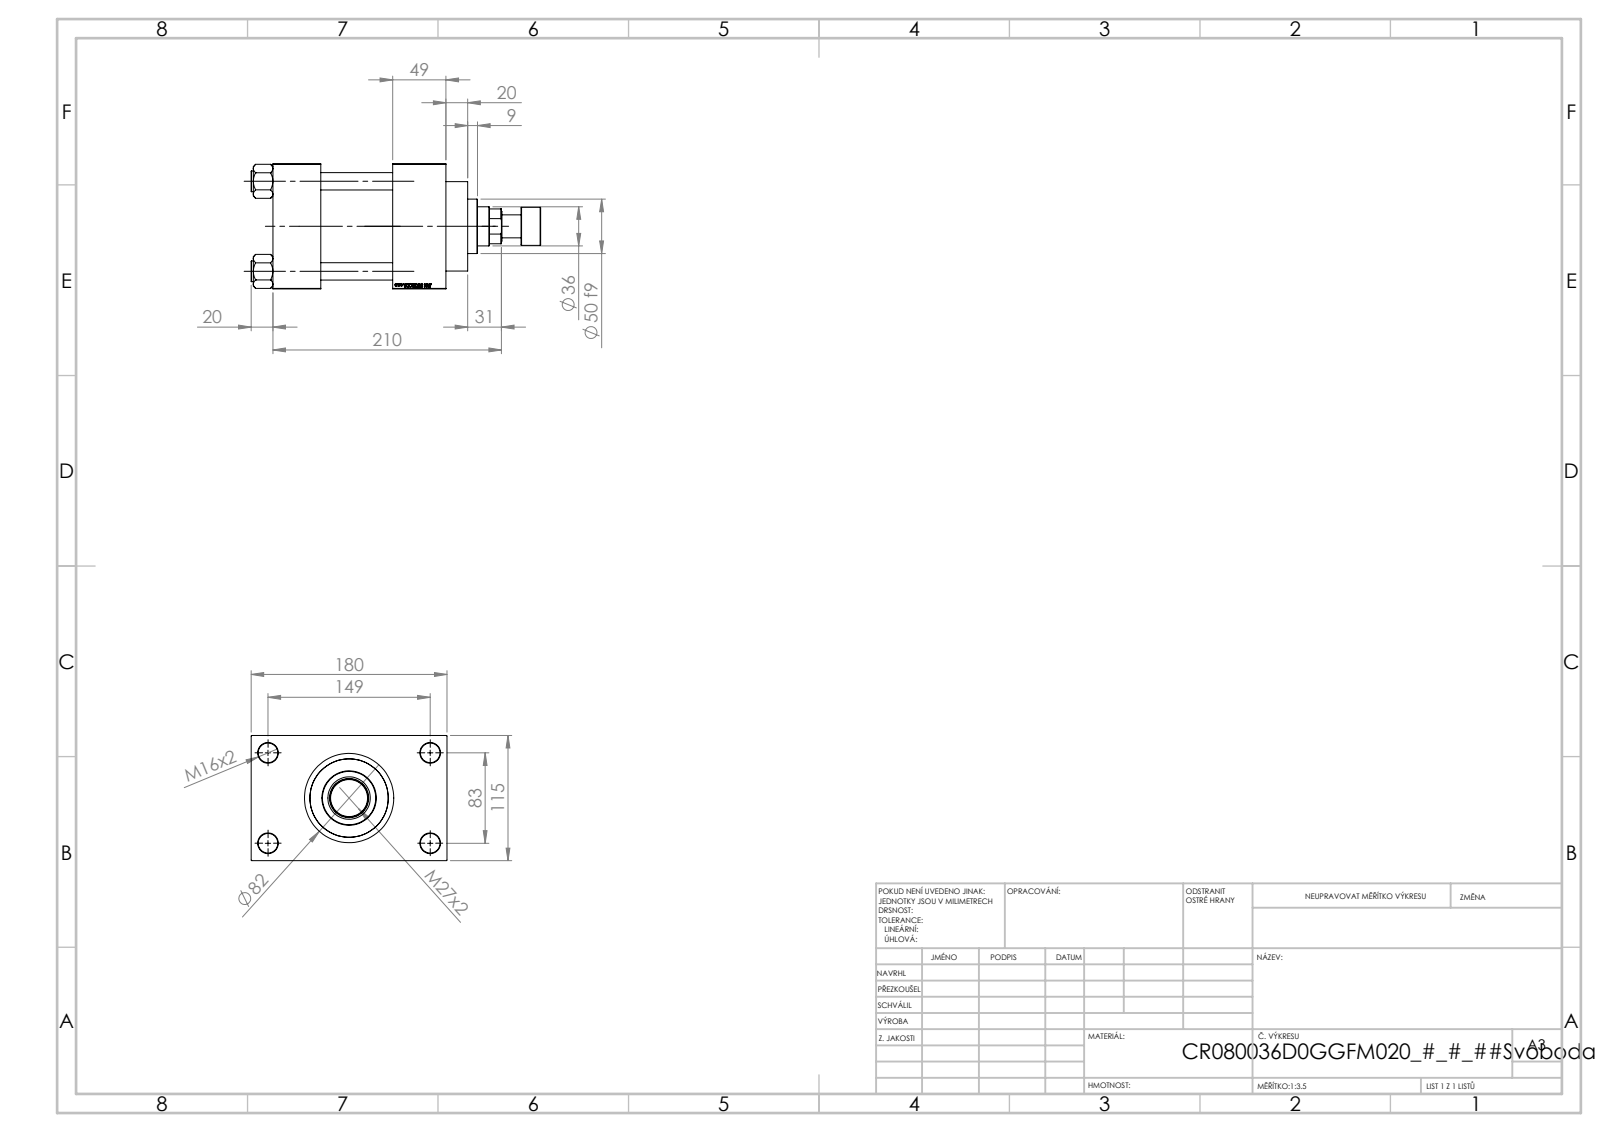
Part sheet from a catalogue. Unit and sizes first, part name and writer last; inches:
Units: inches
Overall size (bounding box): 10.472 × 7.087 × 4.528
Round holes (diameter × count): ⌀0.63 ×4, ⌀0.709 ×4, ⌀0.276 ×2, ⌀1.041 ×2, ⌀1.378 ×2, ⌀1.004 ×1, ⌀1.417 ×1, ⌀1.535 ×1, ⌀2.402 ×1, ⌀2.835 ×1, ⌀3.15 ×1
Round bosses / shafts (diameter × count): ⌀0.748 ×4, ⌀3.386 ×1, ⌀3.228 ×1, ⌀1.969 ×1, ⌀1.378 ×1, ⌀0.827 ×1
Main face-to-face distances: 4.528, 2.598, 1.929, 4.331, 1.732, 6.26, 1.28, 5.807, 0.787, 2.717
Hole centre spacings: 1.305, 2.302, 3.256, 3.357, 3.513, 4.561, 5.607, 3.268
Volume: 123.3 in³ · Surface area: 464.2 in²
Bodies: 12 solids, 1166 faces (549 planar, 93 cylindrical, 524 other)
Part name (STEP PRODUCT): V215CR_D_Body; V215CR_ROD_END_F; NUT_M5_D; V215CR_VCP_D (+2 more)
STEP written by: SolidWorks 2019 (CONFIG_CONTROL_DESIGN)
